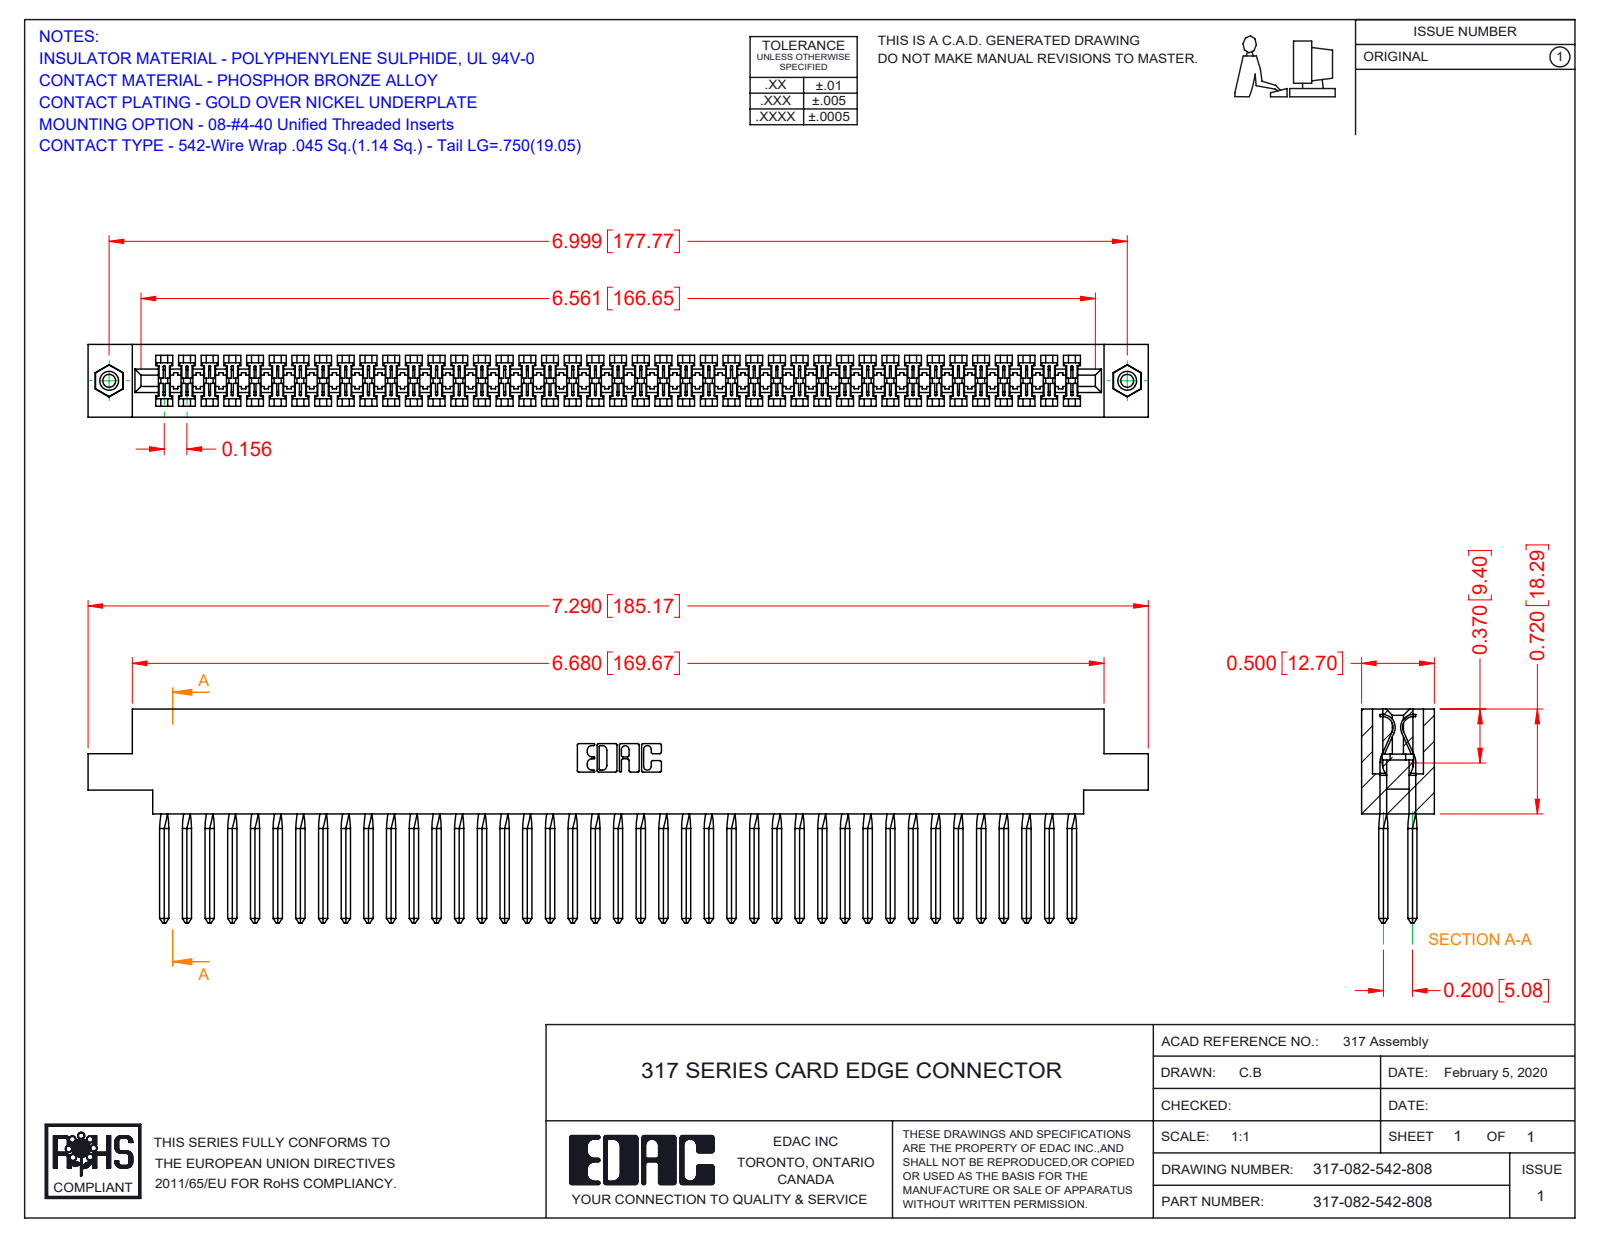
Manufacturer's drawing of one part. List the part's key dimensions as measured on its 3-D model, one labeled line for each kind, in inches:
Part name (STEP PRODUCT): 317-290-003_542; 317-082-542-878; 345-250-001_345-250-003-102; 317 Part_.156 Dia - TI
STEP written by: SolidWorks 2016 (CONFIG_CONTROL_DESIGN)
Units: inches
Bodies: 85 solids, 4836 faces (3862 planar, 630 cylindrical, 344 other)
Overall size (bounding box): 7.29 × 1.47 × 0.5
Volume: 1.848 in³ · Surface area: 65.26 in²
Round holes (diameter × count): ⌀0.089 ×2, ⌀0.125 ×2, ⌀0.156 ×2
Round bosses / shafts (diameter × count): ⌀0.155 ×2
Partial cylindrical surfaces — rounded edges, fillets, slot ends (radius × count): R0.006 ×164, R0.01 ×22, R0.007 ×6, R0.031 ×6, R0.026 ×3, R0.074 ×2, R0.089 ×2, R0.1 ×2
Main face-to-face distances: 0.5, 0.075, 0.425, 0.35, 0.2, 0.046, 0.128, 0.372, 0.052, 0.297
Hole centre spacings: 6.999
